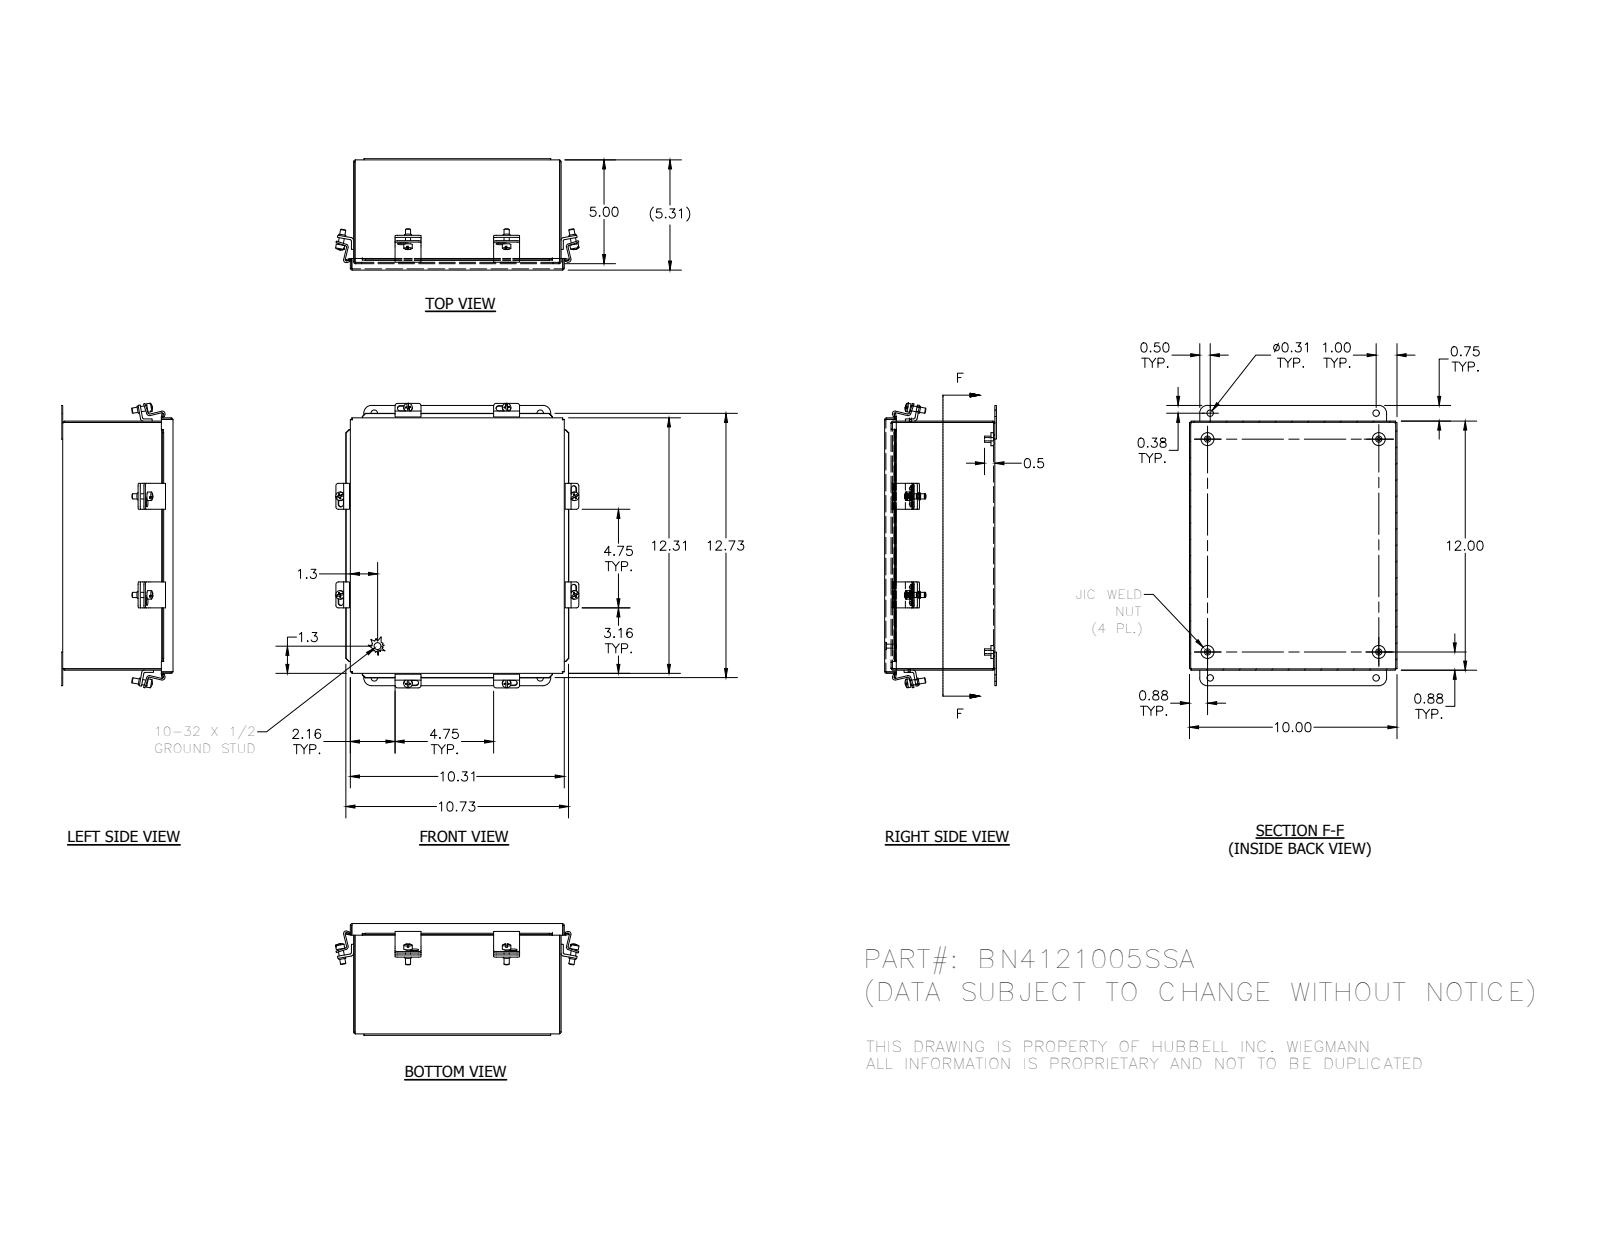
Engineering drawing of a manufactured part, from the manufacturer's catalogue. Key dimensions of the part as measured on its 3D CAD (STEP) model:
Part name (STEP PRODUCT): 30810_1; 30811_1; BN41210SSALID_1; 372164_1 (+5 more)
STEP written by: SolidWorks 2014 (AUTOMOTIVE_DESIGN)
Units: inches
Bodies: 33 solids, 917 faces (439 planar, 328 cylindrical, 150 other)
Overall size (bounding box): 13.713 × 11.724 × 5.388
Volume: 36.53 in³ · Surface area: 1 148 in²
Round holes (diameter × count): ⌀0.11 ×12, ⌀0.196 ×8, ⌀0.156 ×4, ⌀0.31 ×4
Round bosses / shafts (diameter × count): ⌀0.41 ×8, ⌀0.344 ×8, ⌀0.25 ×8, ⌀0.625 ×4, ⌀0.3 ×4, ⌀0.337 ×1, ⌀0.19 ×1
Partial cylindrical surfaces — rounded edges, fillets, slot ends (radius × count): R0.125 ×32, R0.031 ×16, R0.094 ×16, R0.133 ×16, R0.063 ×12, R0.126 ×12, R0.375 ×4
Main face-to-face distances: 0.063, 5.25, 5.313, 5.187, 9.937, 11.937, 10, 9.875, 12, 11.875
Hole centre spacings: 4.75, 0.75, 0.063, 0.753, 1.256, 4.75, 11.501, 14.081
